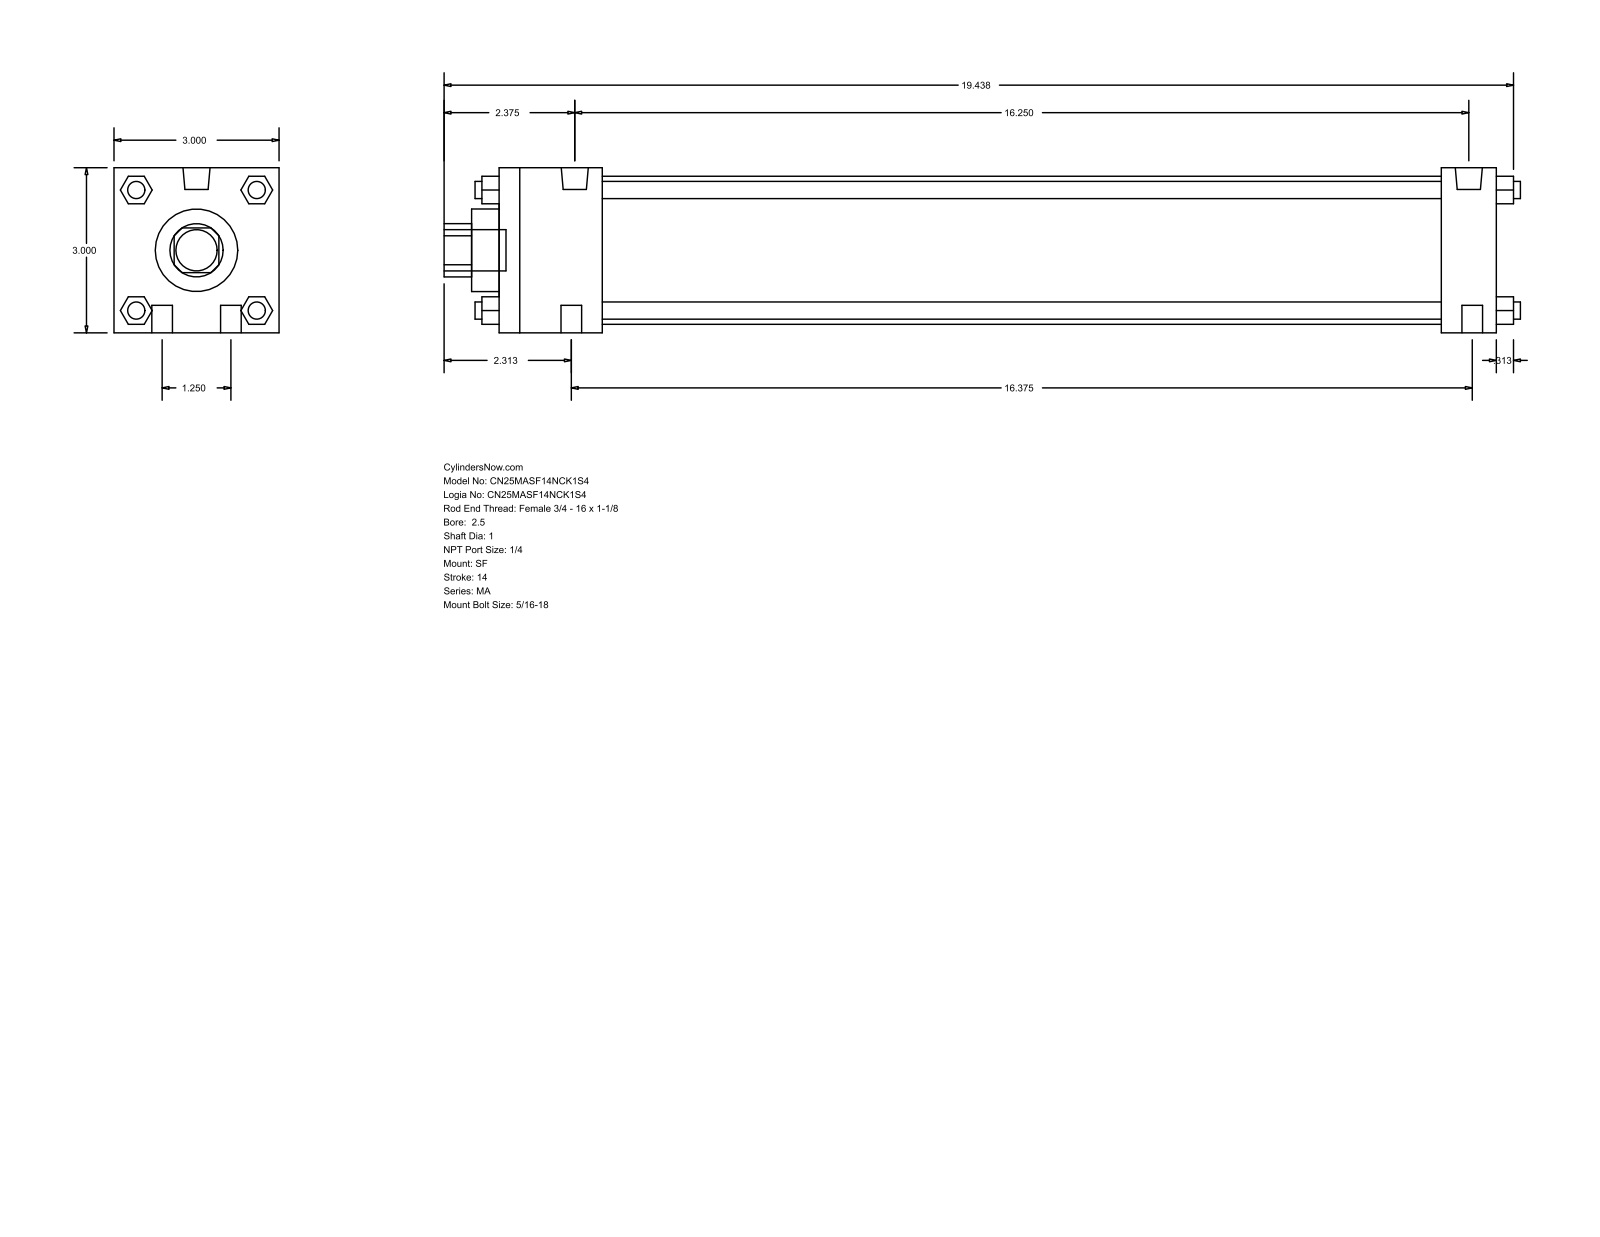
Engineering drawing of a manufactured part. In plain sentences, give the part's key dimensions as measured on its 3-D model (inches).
The part is named "MA_SF__0250_1". Its 3-D file was written by "GSSL Pune (CONFIG_CONTROL_DESIGN)". It is 0 solids with 124 faces: 94 planar, 30 cylindrical and 0 other. Overall it measures 19.563 by 3 by 3 inches. Round holes: 1 of diameter 1, 1 of diameter 1.5, 1 of diameter 2.69. Round bosses or shafts: 6 of diameter 0.313, 4 of diameter 0.375, 2 of diameter 0.492, 1 of diameter 0.75. Partial cylindrical surfaces (rounded edges, fillets, slot ends): 1 of radius 0.484. The main face-to-face distances are 3, 18.125, 0.5, 17.125, 1, 1.875, 15.25, 16.25, 1.095, 1.896.
